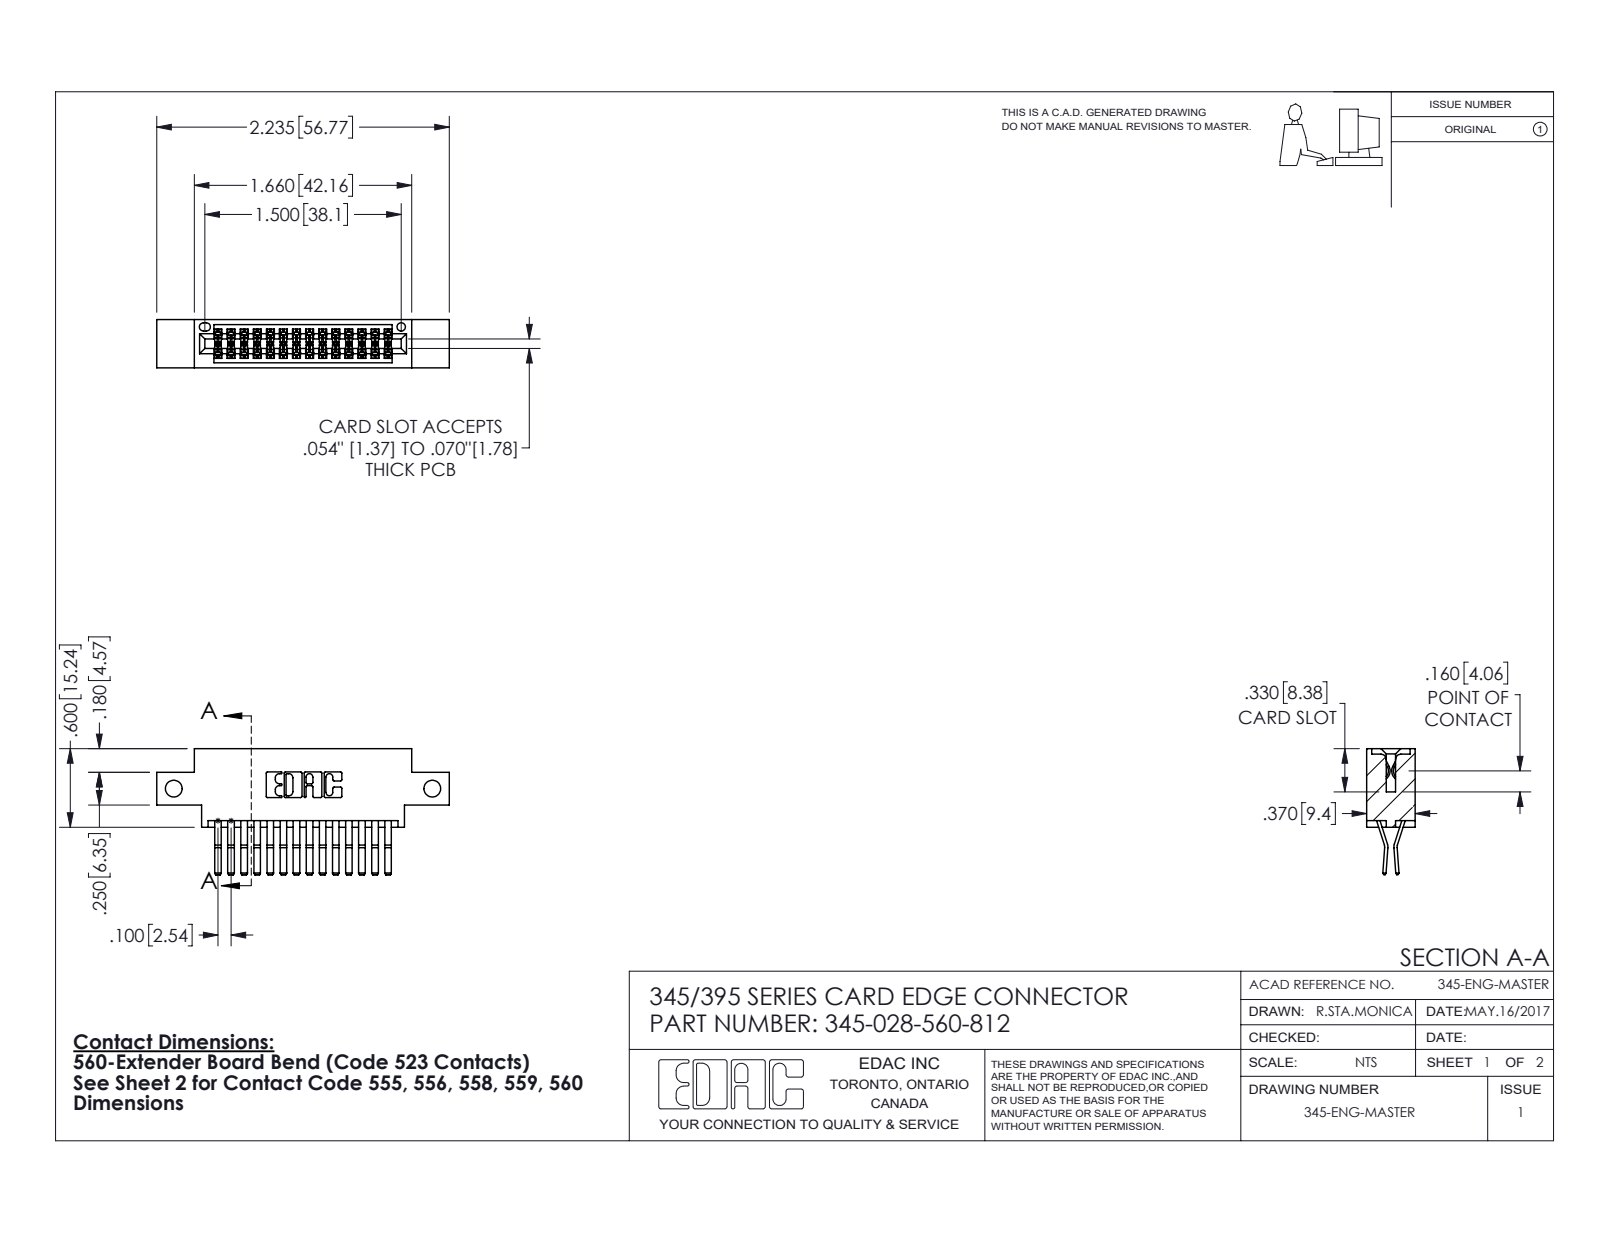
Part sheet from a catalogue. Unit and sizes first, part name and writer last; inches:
Units: inches
Overall size (bounding box): 2.235 × 0.962 × 0.37
Round holes (diameter × count): ⌀0.128 ×2, ⌀0.064 ×1
Partial cylindrical surfaces — rounded edges, fillets, slot ends (radius × count): R0.006 ×43, R0.01 ×22, R0.007 ×6, R0.031 ×6, R0.026 ×3, R0.01 ×2, R0.014 ×2, R0.019 ×2
Main face-to-face distances: 0.025, 0.298, 0.072, 0.37, 0.2, 0.098, 0.272, 0.225, 0.1, 0.175
Hole centre spacings: 1.975
Volume: 0.32 in³ · Surface area: 11.9 in²
Bodies: 29 solids, 1586 faces (1008 planar, 578 cylindrical, 0 other)
Part name (STEP PRODUCT): 345-292-001_560 Tail; 345 Part_0.170 Offset - Side Mount; 345-028-560-812
STEP written by: SolidWorks 2016 (CONFIG_CONTROL_DESIGN)
